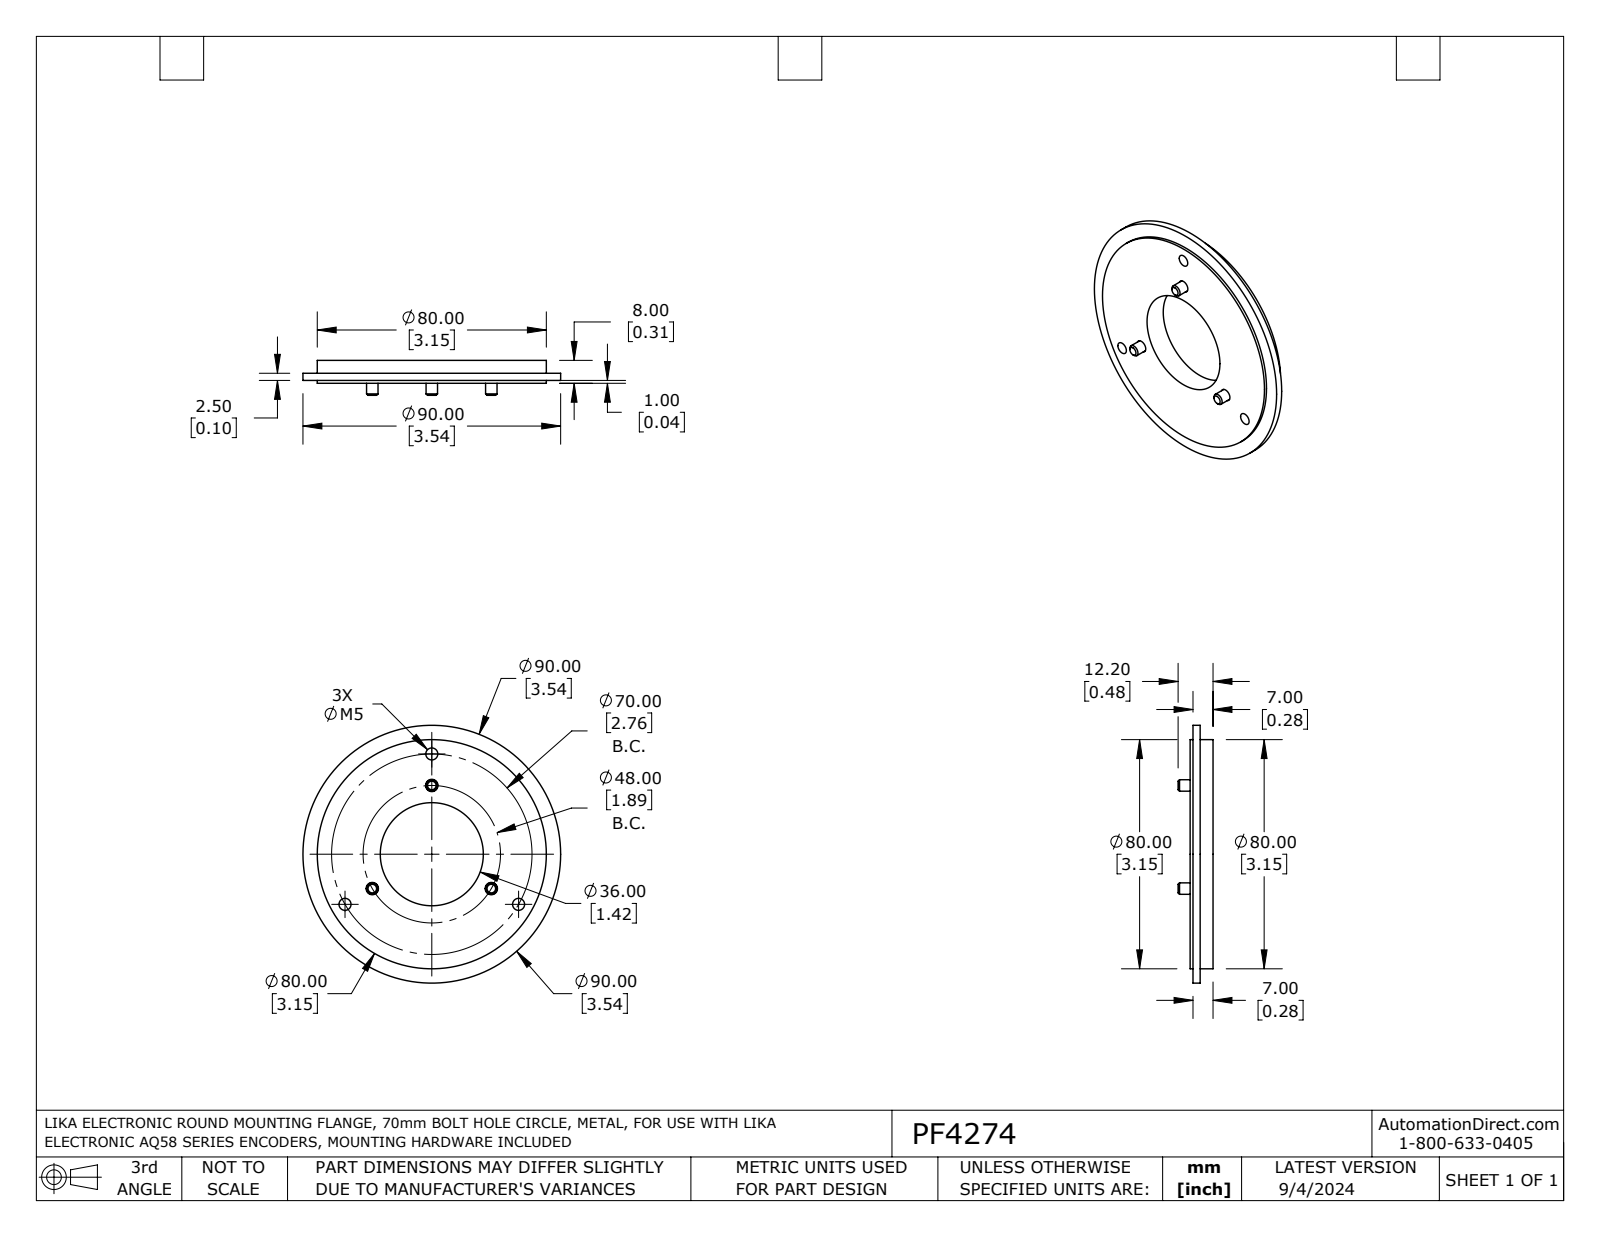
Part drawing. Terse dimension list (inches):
name: PF4274
written by: SolidWorks 2021 (AUTOMOTIVE_DESIGN)
unit: in
bodies: 4 solids, 111 faces (37 planar, 56 cylindrical, 18 other)
size: 3.543 × 3.543 × 0.48
volume: 2.143 in³; area: 23.44 in²
holes: 3× ⌀0.165, 3× ⌀0.169, 3× ⌀0.276, 1× ⌀1.417
bosses: 3× ⌀0.157, 1× ⌀3.543, 1× ⌀3.15
rounds: 18× R0.008
face distances: 0.315, 0.039, 0.177, 0.276, 0.098, 0.138, 0.15, 0.165, 0.11, 0.157
hole spacings: 2.023, 0.433, 0.945, 1.378, 2.387, 1.637, 1.636
